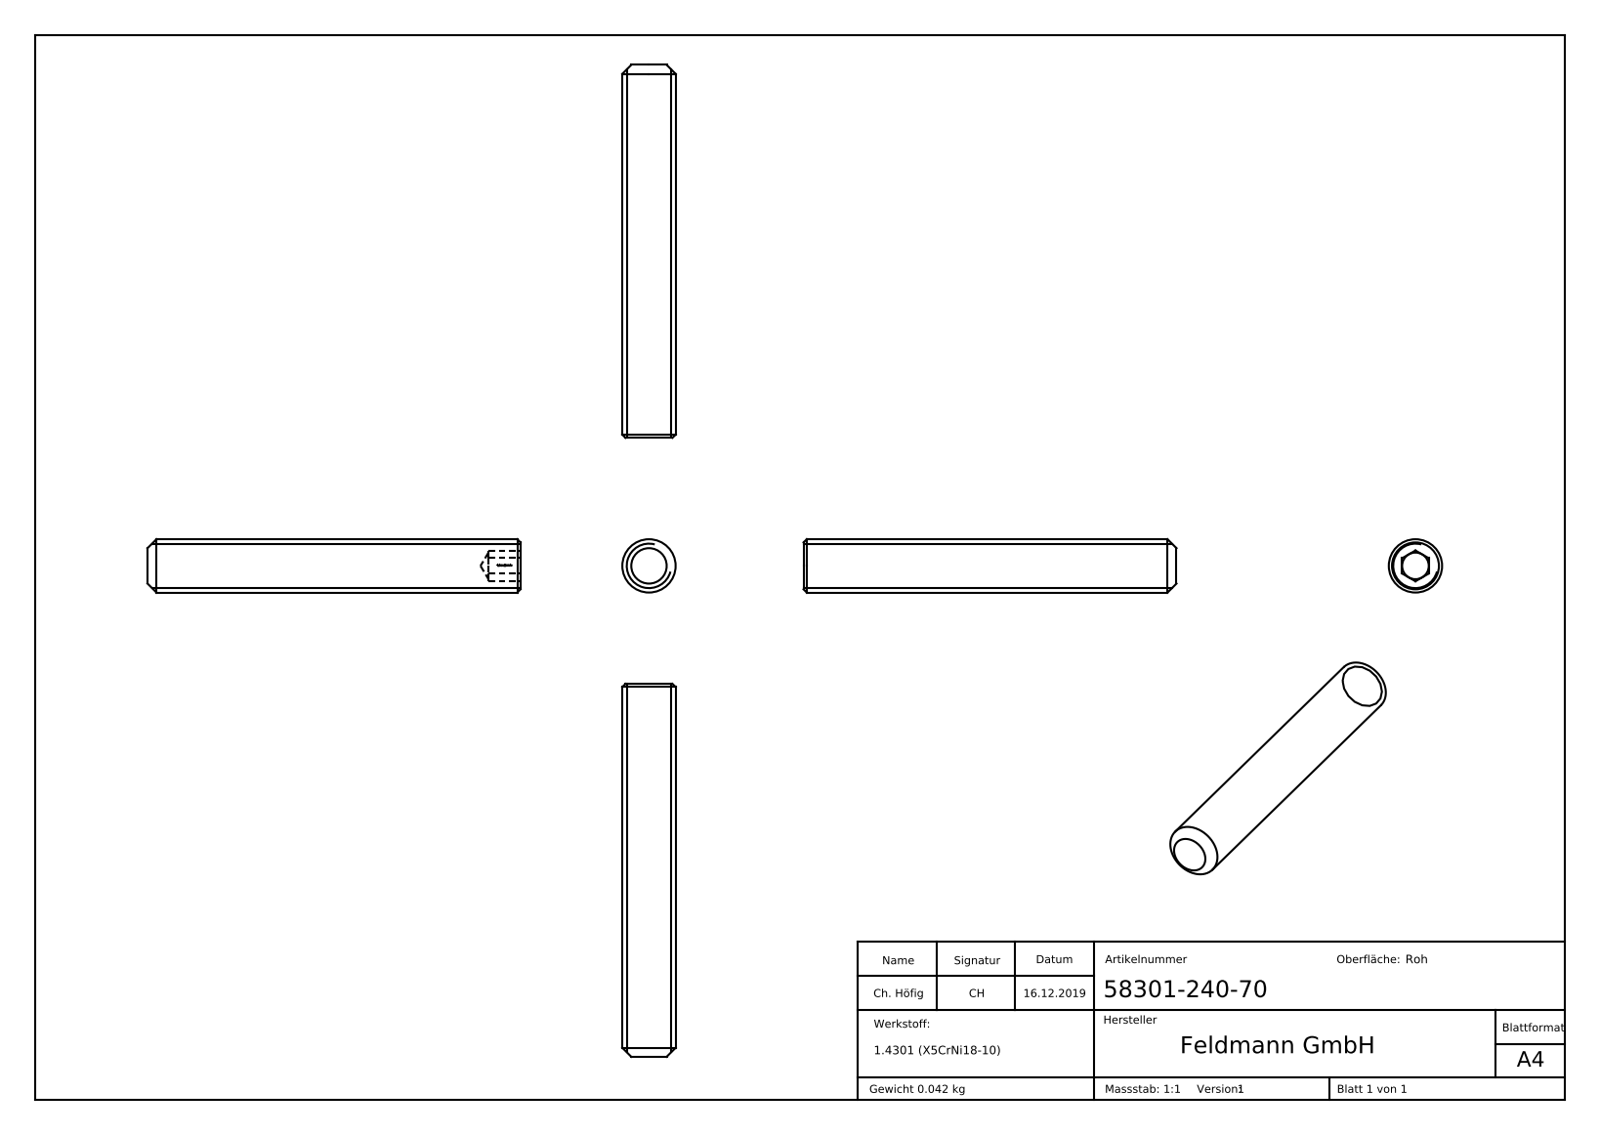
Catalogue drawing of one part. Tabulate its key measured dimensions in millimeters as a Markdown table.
| quantity | value |
| --- | --- |
| part name | 58301-240-70 |
| STEP written by | SolidWorks 2015 (CONFIG_CONTROL_DESIGN) |
| units | millimeters |
| bodies | 1 solid, 284 faces (142 planar, 1 cylindrical, 141 other) |
| overall size | 110 × 10 × 10 |
| volume | 5 313 mm³ |
| surface area | 2 419 mm² |
| round bosses / shafts (diameter × count) | 10 × 1 |
| main face-to-face distances | 5, 70, 64, 6, 5.1, 0.37, 0.48, 0.54, 0.82, 0.96 |
